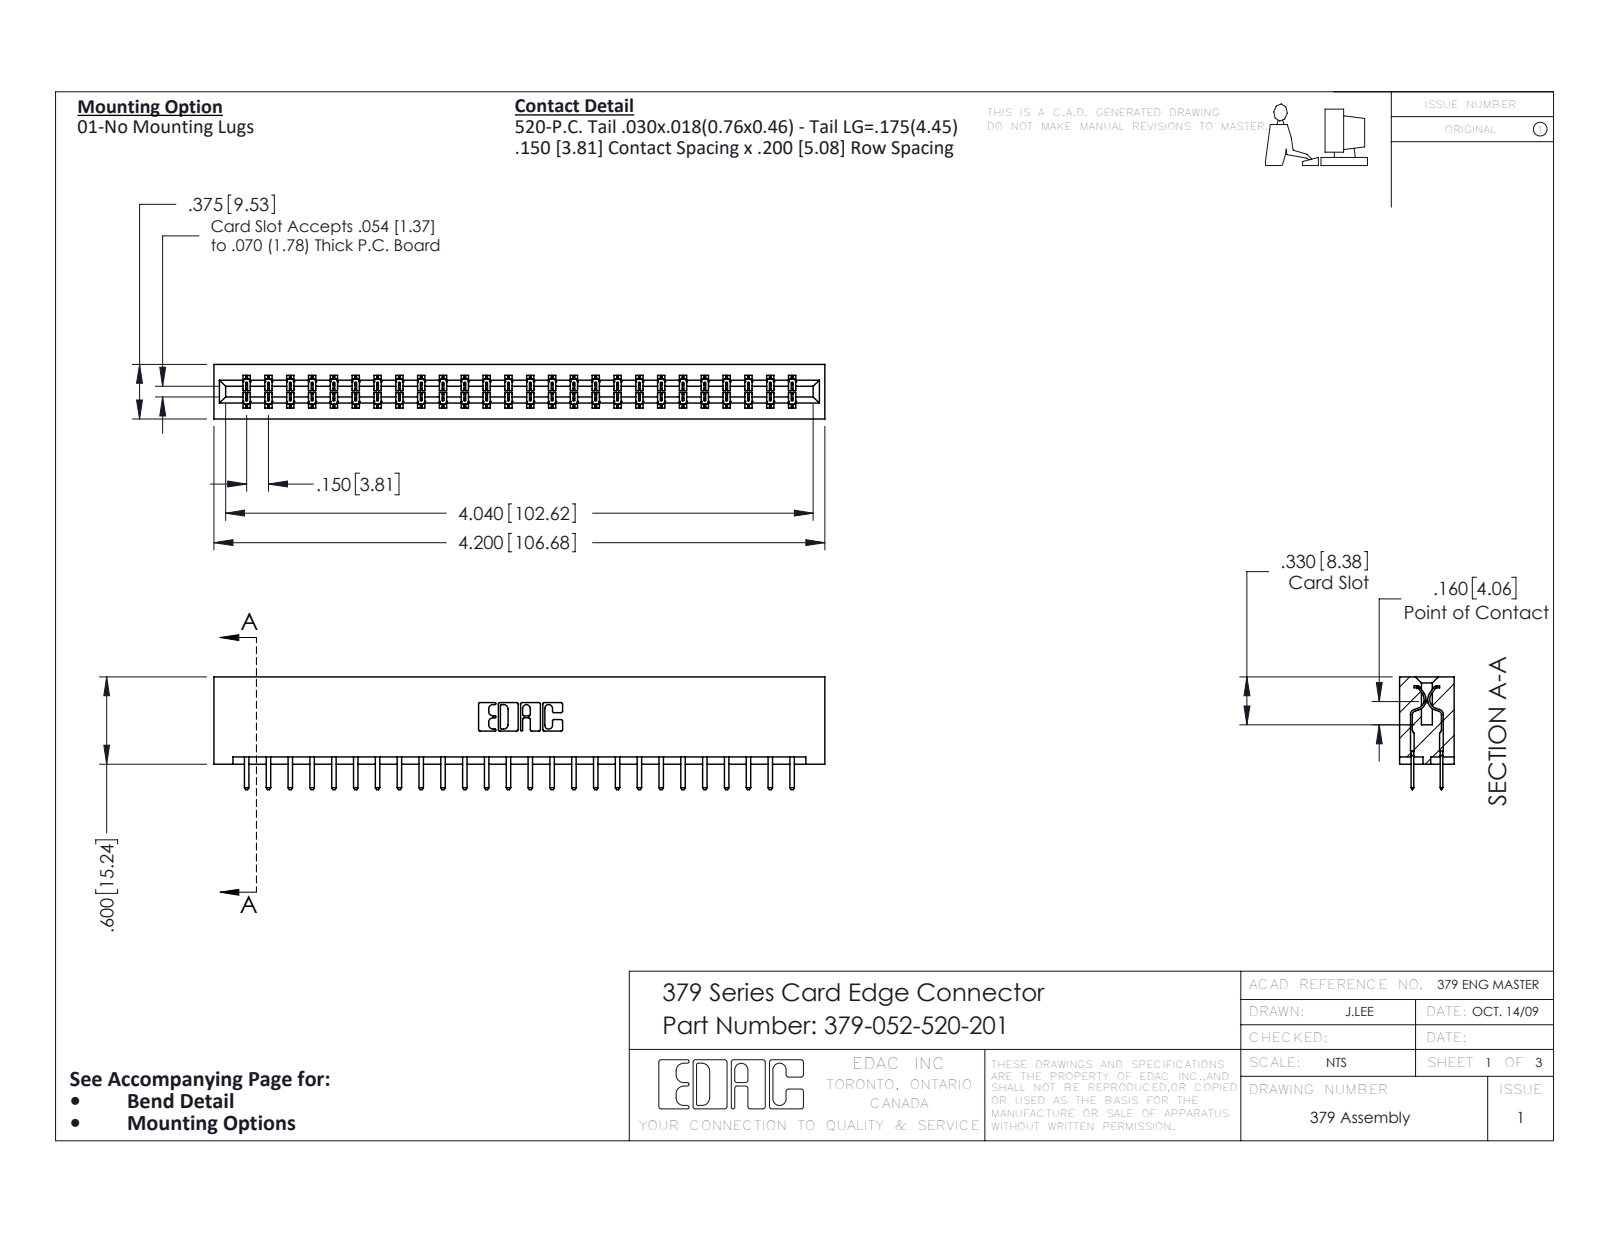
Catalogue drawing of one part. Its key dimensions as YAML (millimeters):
part_name: "345-292-001_345-293-120; 379 Part_Lugless; 379-052-520-201"
step_written_by: "SolidWorks 2016 (CONFIG_CONTROL_DESIGN)"
units: millimeters
bodies: {solids: 53, faces: 3018, planar: 2042, cylindrical: 976, other: 0}
overall_size: [106.7, 19.7, 9.5]
volume: 11900
surface_area: 13170
partial_cylinders:
  - {radius: 0.2, count: 78}
  - {radius: 0.3, count: 56}
  - {radius: 0.3, count: 22}
  - {radius: 0.2, count: 6}
  - {radius: 0.8, count: 6}
  - {radius: 0.7, count: 3}
  - {radius: 0.4, count: 2}
  - {radius: 0.6, count: 2}
face_to_face_distances: [7.6, 1.9, 9.5, 5.1, 5.7, 2.5, 14, 3.8, 3.8, 1.9]
